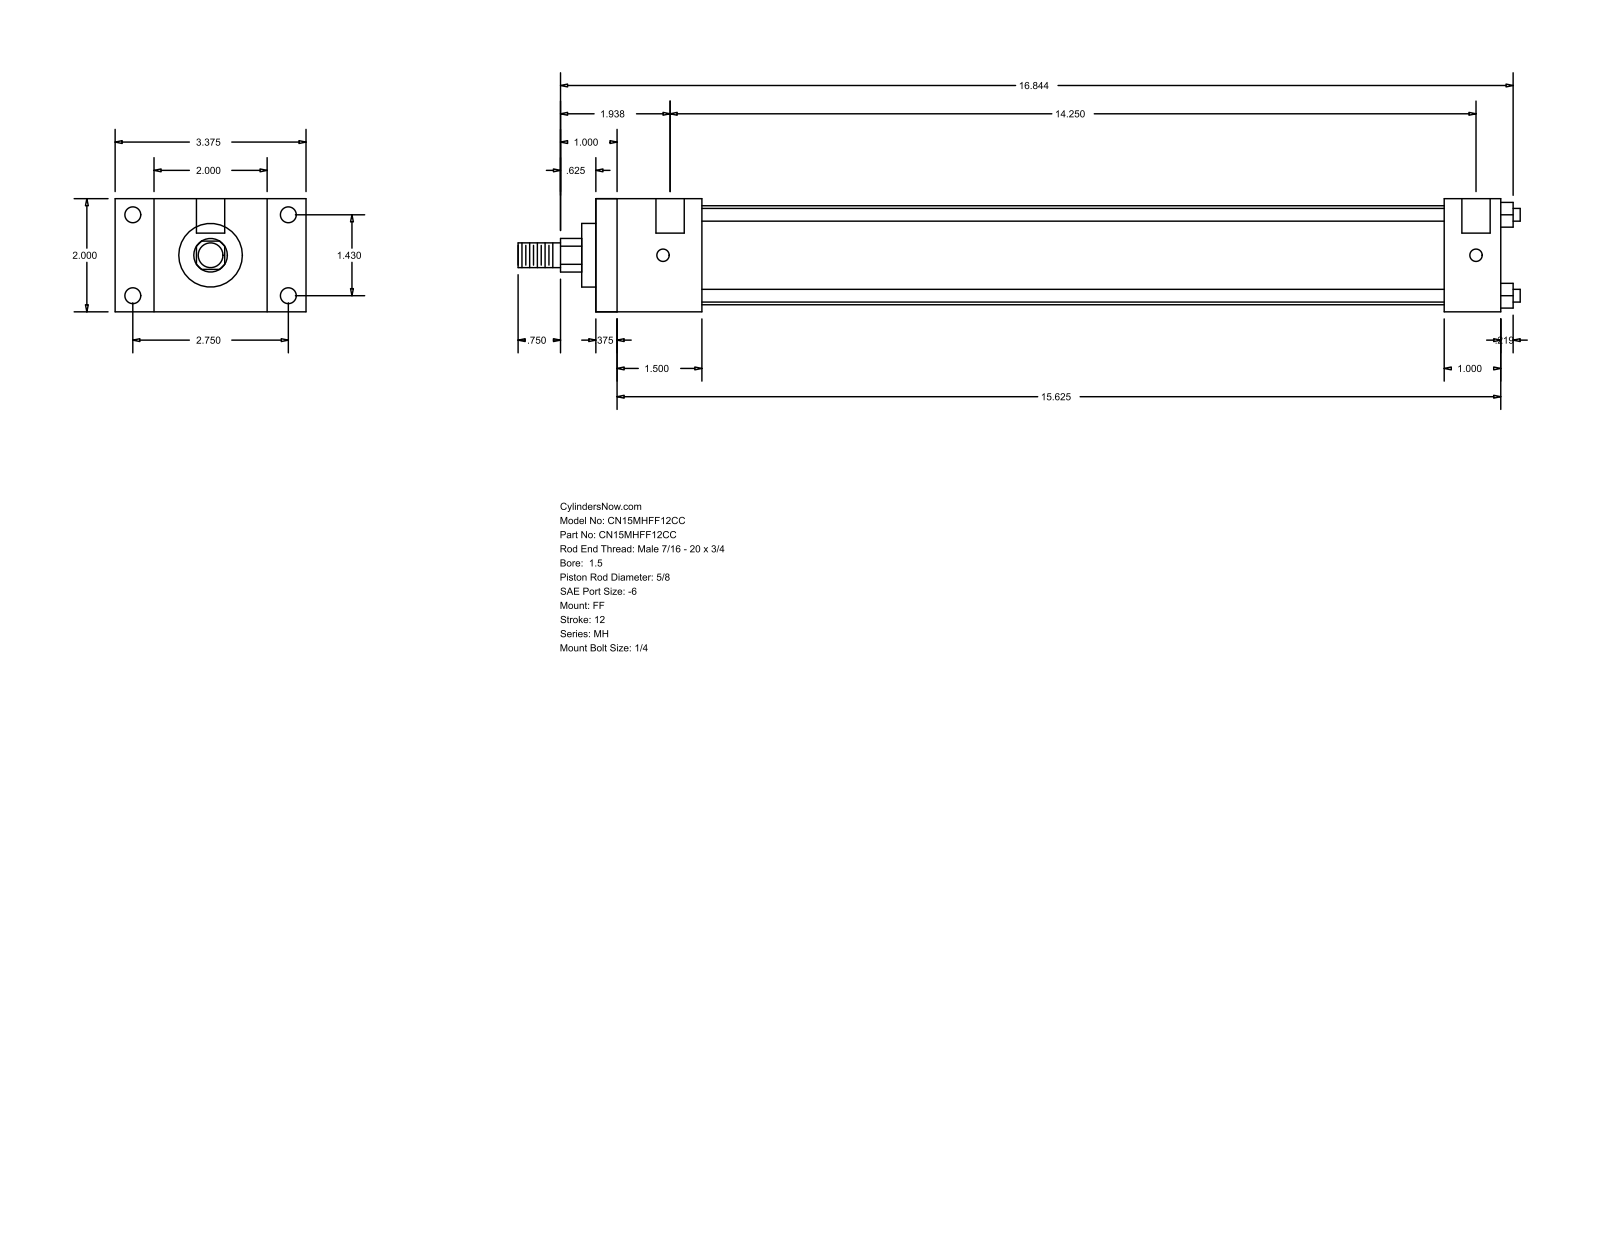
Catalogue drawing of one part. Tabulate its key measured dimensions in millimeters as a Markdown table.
| quantity | value |
| --- | --- |
| part name | MH_FF__0150_0.625 |
| STEP written by | GSSL Pune (CONFIG_CONTROL_DESIGN) |
| units | millimeters |
| bodies | 0 solids, 92 faces (64 planar, 28 cylindrical, 0 other) |
| overall size | 450.06 × 85.72 × 50.8 |
| round holes (diameter × count) | 5.56 × 4, 7.14 × 4, 12.7 × 2 |
| round bosses / shafts (diameter × count) | 5.71 × 4, 44.45 × 1, 28.57 × 1, 15.88 × 1, 11.11 × 1 |
| partial cylindrical surfaces (radius × count) | 7.54 × 1 |
| main face-to-face distances | 50.8, 406.39, 9.52, 396.87, 17.46, 68.26, 47.62, 38.1, 358.77, 381 |
| hole center spacings | 36.32, 69.84, 78.72, 365.12, 3.17, 361.95 |
